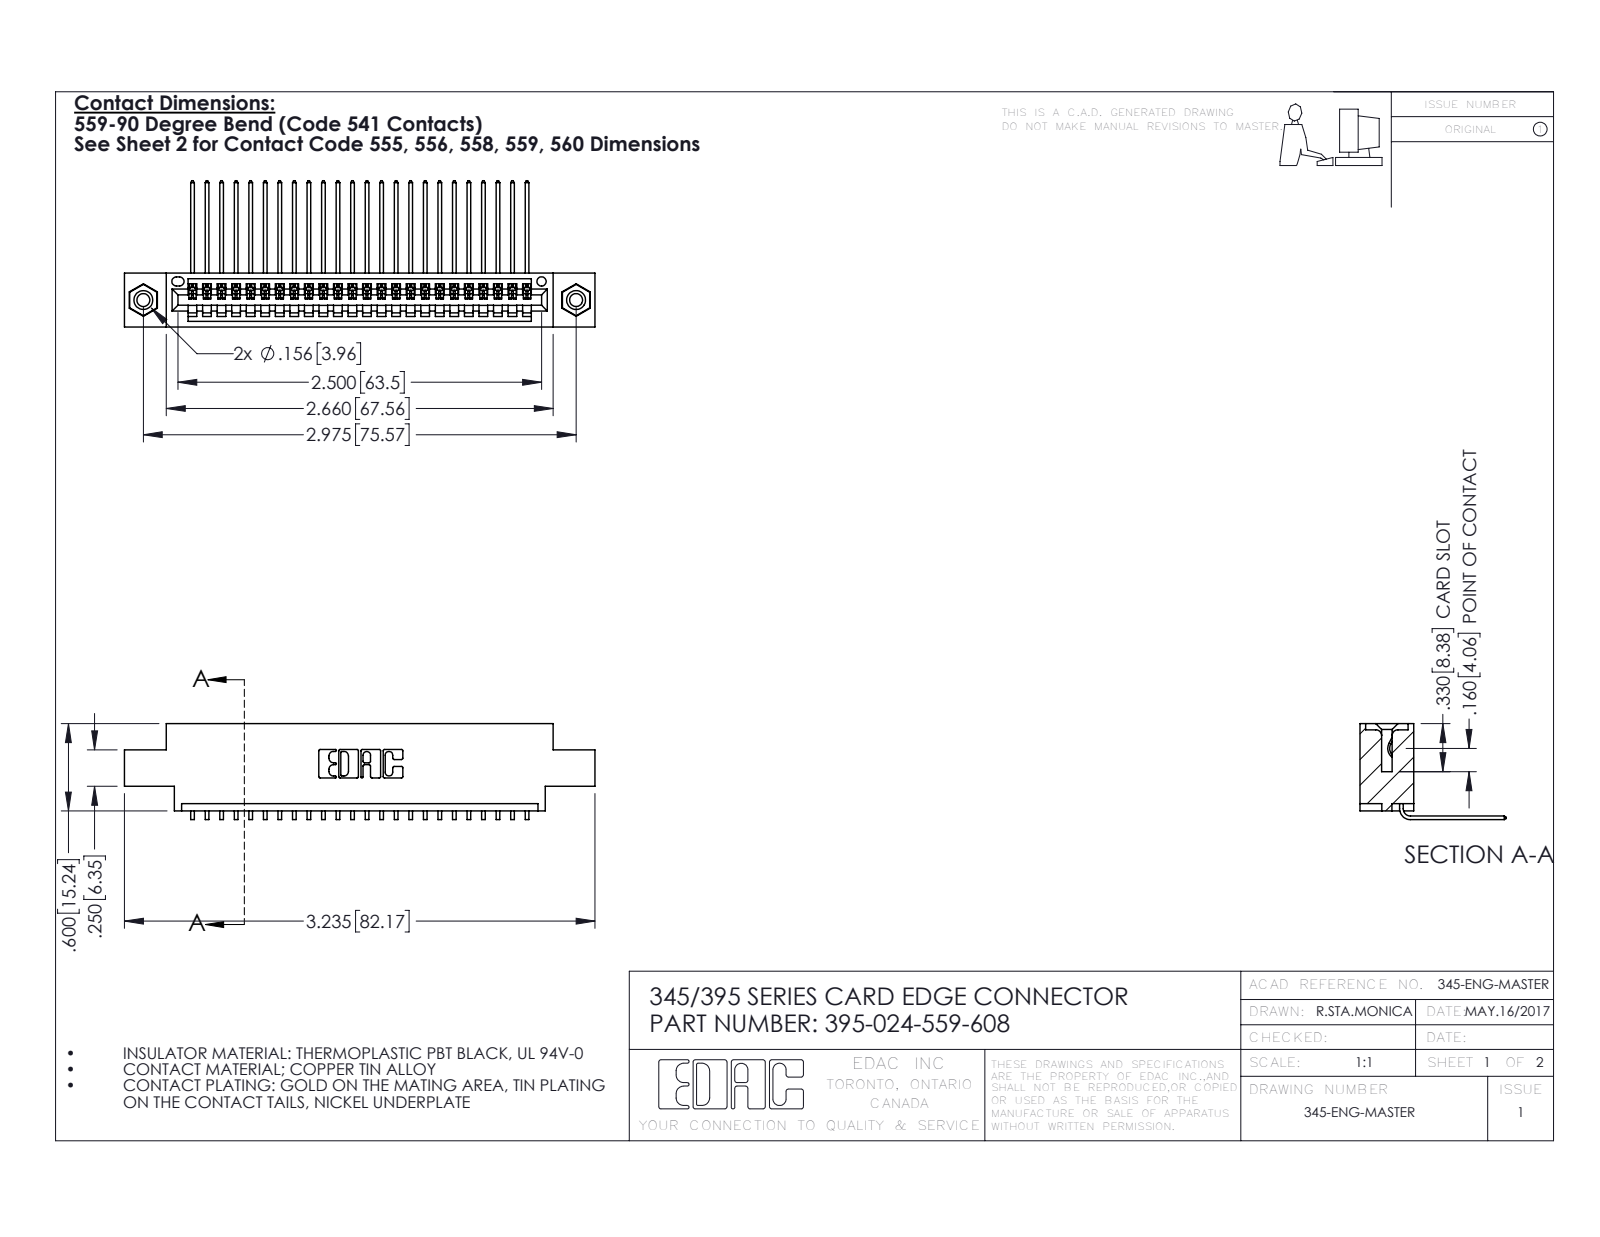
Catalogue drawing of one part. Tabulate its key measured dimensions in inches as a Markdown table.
| quantity | value |
| --- | --- |
| part name | 395-024-559-608; 345-250-001_345-250-003-102; 345-292-001_558 559 Tail - 1; 345 Part_0.170 Offset - 0.156 Dia-TI |
| STEP written by | SolidWorks 2016 (CONFIG_CONTROL_DESIGN) |
| units | inches |
| bodies | 27 solids, 1630 faces (1124 planar, 490 cylindrical, 16 other) |
| overall size | 3.235 × 1.005 × 0.659 |
| volume | 0.465 in³ |
| surface area | 16.26 in² |
| round holes (diameter × count) | 0.089 × 2, 0.125 × 2, 0.156 × 2, 0.064 × 1 |
| round bosses / shafts (diameter × count) | 0.155 × 2 |
| partial cylindrical surfaces (radius × count) | 0.006 × 48, 0.01 × 22, 0.007 × 6, 0.031 × 6, 0.026 × 3, 0.031 × 2, 0.04 × 2, 0.014 × 1 |
| main face-to-face distances | 0.072, 0.298, 0.37, 0.2, 0.098, 0.272, 0.025, 0.225, 0.175, 0.149 |
| hole center spacings | 0.27, 2.741, 2.975 |
